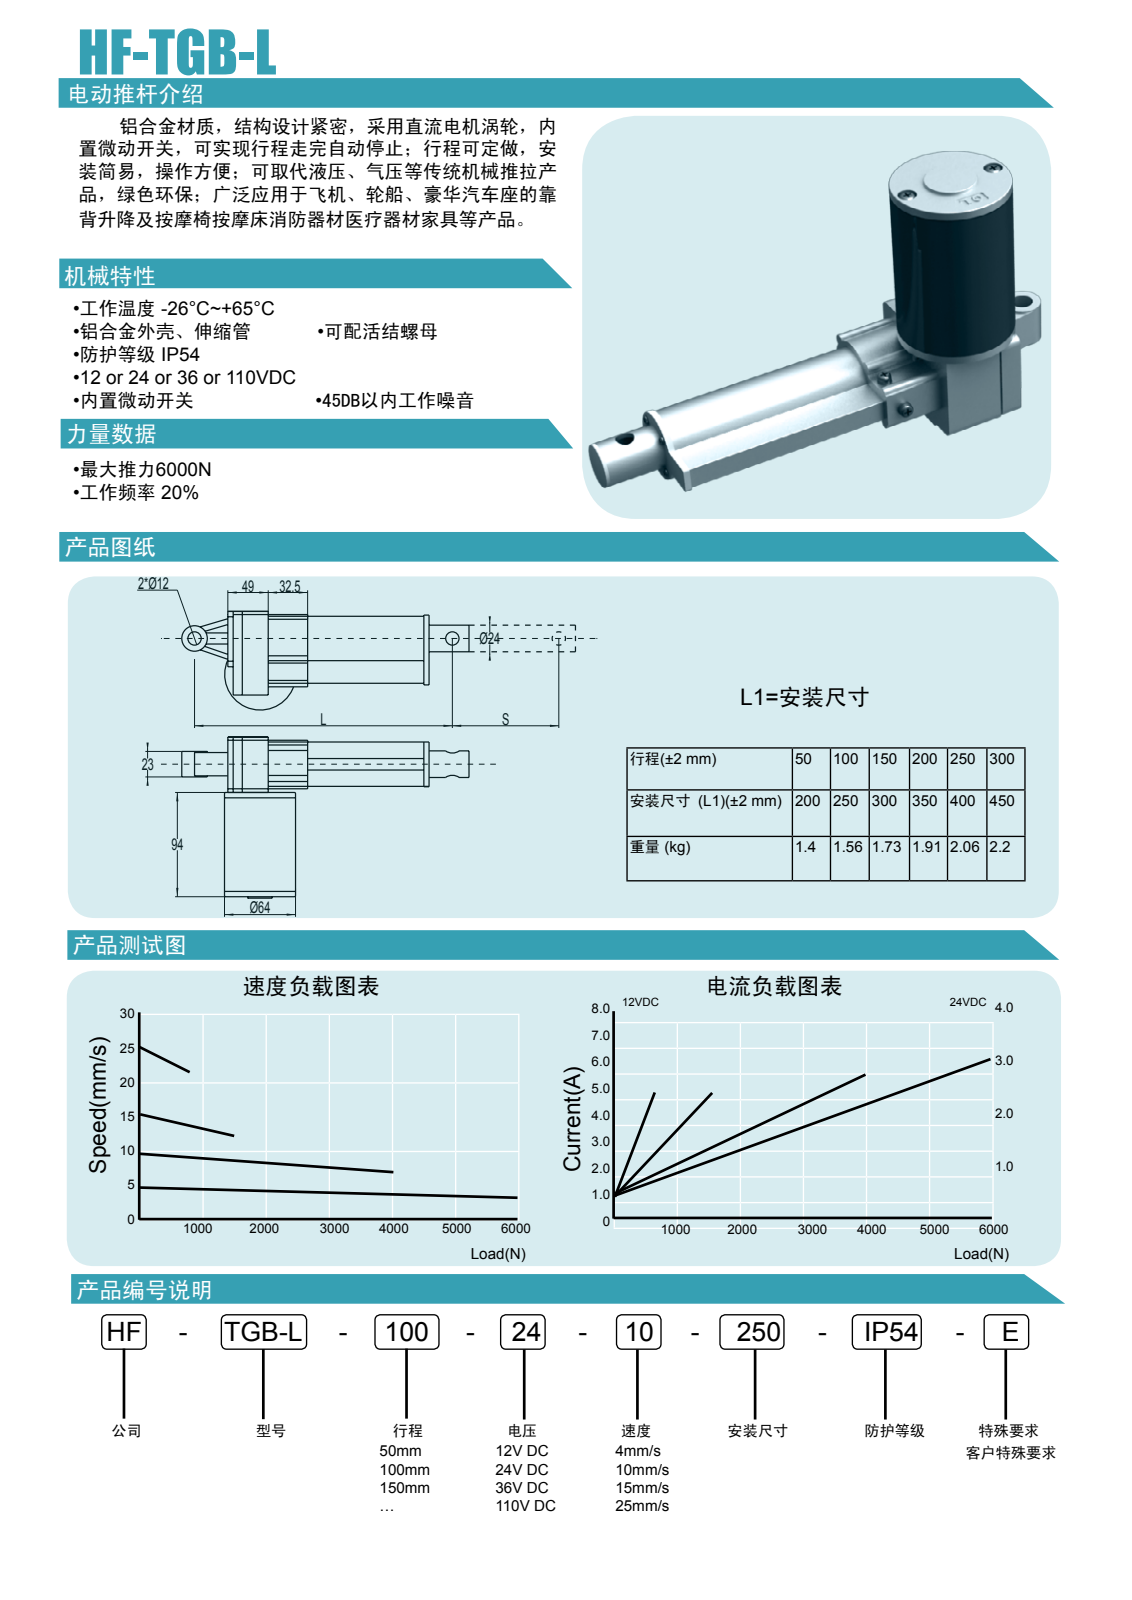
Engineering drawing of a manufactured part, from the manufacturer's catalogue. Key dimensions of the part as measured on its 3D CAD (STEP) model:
Part name (STEP PRODUCT): DZ; DZ-1; DZ-ZG; DZ-SG (+6 more)
STEP written by: PRO/ENGINEER BY PARAMETRIC TECHNOLOGY CORPORATION, 2008380 (CONFIG_CONTROL_DESIGN)
Units: millimetres
Bodies: 9 solids, 164 faces (81 planar, 77 cylindrical, 6 other)
Overall size (bounding box): 278.5 × 144.03 × 80
Volume: 544 428 mm³ · Surface area: 142 033 mm²
Round holes (diameter × count): ⌀5 ×7, ⌀8 ×2, ⌀9 ×2, ⌀12 ×2, ⌀22 ×1, ⌀25 ×1, ⌀31 ×1, ⌀37.03 ×1
Round bosses / shafts (diameter × count): ⌀64 ×1, ⌀39 ×1, ⌀37 ×1, ⌀28 ×1, ⌀22 ×1
Partial cylindrical surfaces — rounded edges, fillets, slot ends (radius × count): R5 ×7, R3 ×5, R2 ×2, R1.28 ×1, R1.5 ×1, R10.91 ×1, R21.5 ×1
Main face-to-face distances: 12, 2.99, 9, 40, 35, 23, 17, 5, 33.01, 91
Hole centre spacings: 40.99, 40, 41, 0.99, 29.5, 40.71, 57.28, 57.97
